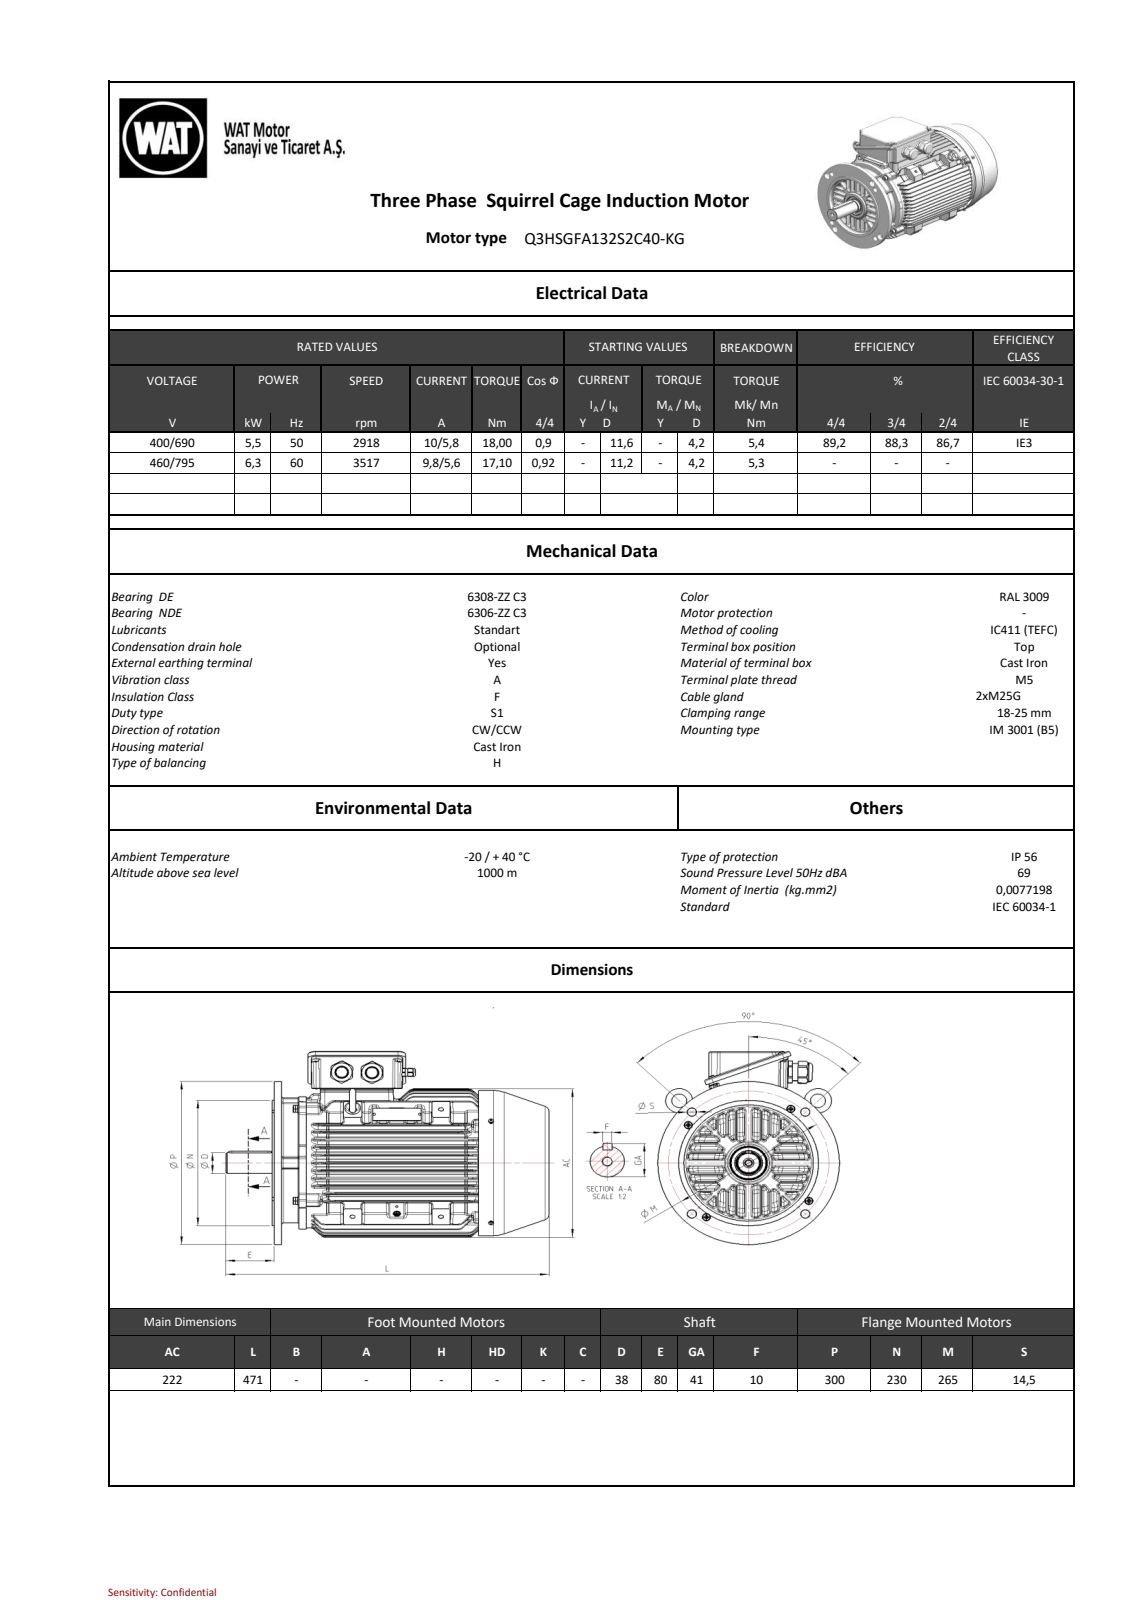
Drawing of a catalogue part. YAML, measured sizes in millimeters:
part_name: "26005FFCEC27c7pq"
step_written_by: "SIEMENS PLM Software NX 11.0 (AUTOMOTIVE_DESIGN)"
units: millimeters
bodies: {solids: 0, faces: 4154, planar: 818, cylindrical: 1188, other: 2148}
overall_size: [471, 328.63, 299]
round_holes:
  - {diameter: 5, count: 10}
  - {diameter: 6.8, count: 6}
  - {diameter: 10, count: 4}
  - {diameter: 12, count: 4}
  - {diameter: 2.5, count: 2}
  - {diameter: 17.2, count: 2}
  - {diameter: 6.3, count: 1}
  - {diameter: 8, count: 1}
  - {diameter: 10.2, count: 1}
  - {diameter: 13, count: 1}
  - {diameter: 58.4, count: 1}
  - {diameter: 58.6, count: 1}
round_bosses_or_shafts:
  - {diameter: 8.65, count: 4}
  - {diameter: 8, count: 4}
  - {diameter: 4, count: 3}
  - {diameter: 27.7, count: 2}
  - {diameter: 25.25, count: 2}
  - {diameter: 20, count: 2}
  - {diameter: 12, count: 2}
  - {diameter: 299, count: 1}
partial_cylinders:
  - {radius: 4, count: 276}
  - {radius: 1.5, count: 96}
  - {radius: 0.5, count: 93}
  - {radius: 3, count: 76}
  - {radius: 2, count: 43}
  - {radius: 1.8, count: 24}
  - {radius: 1, count: 21}
  - {radius: 0.25, count: 17}
face_to_face_distances: [6, 51, 13.1, 26.28, 13.18, 39.54, 26.44, 13.26, 39.96, 90.54]
hole_center_spacings: [65.3, 97, 137.18, 33.69, 38.02, 111.28, 130, 158.92]
